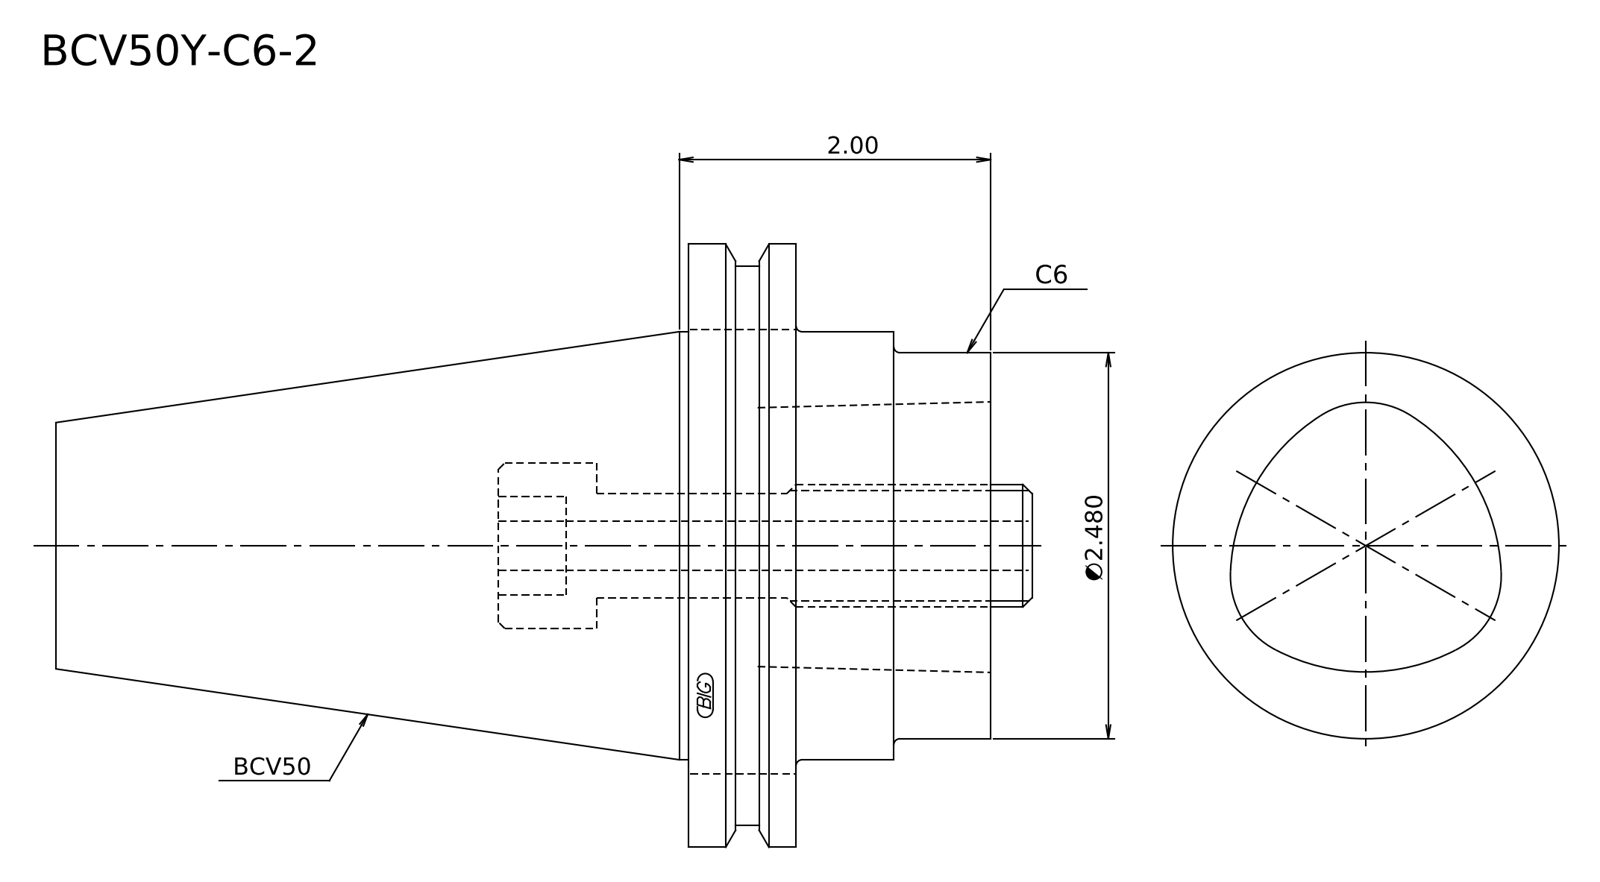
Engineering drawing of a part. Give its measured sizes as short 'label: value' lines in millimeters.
written by: Kubotek KeyCreator 2011 V10.0.2 (22737) (automotive_design)
unit: mm
bodies: 1 solid, 18 faces (7 planar, 6 cylindrical, 5 other)
size: 152.4 × 98.42 × 98.42
volume: 491 941 mm³; area: 43 854 mm²
bosses: 1× ⌀98.42, 1× ⌀91.29, 1× ⌀69.85, 1× ⌀63
face distances: 17.55, 31.75, 49.3, 152.4, 120.65, 103.1, 15.8, 15.95, 33.5, 136.6
